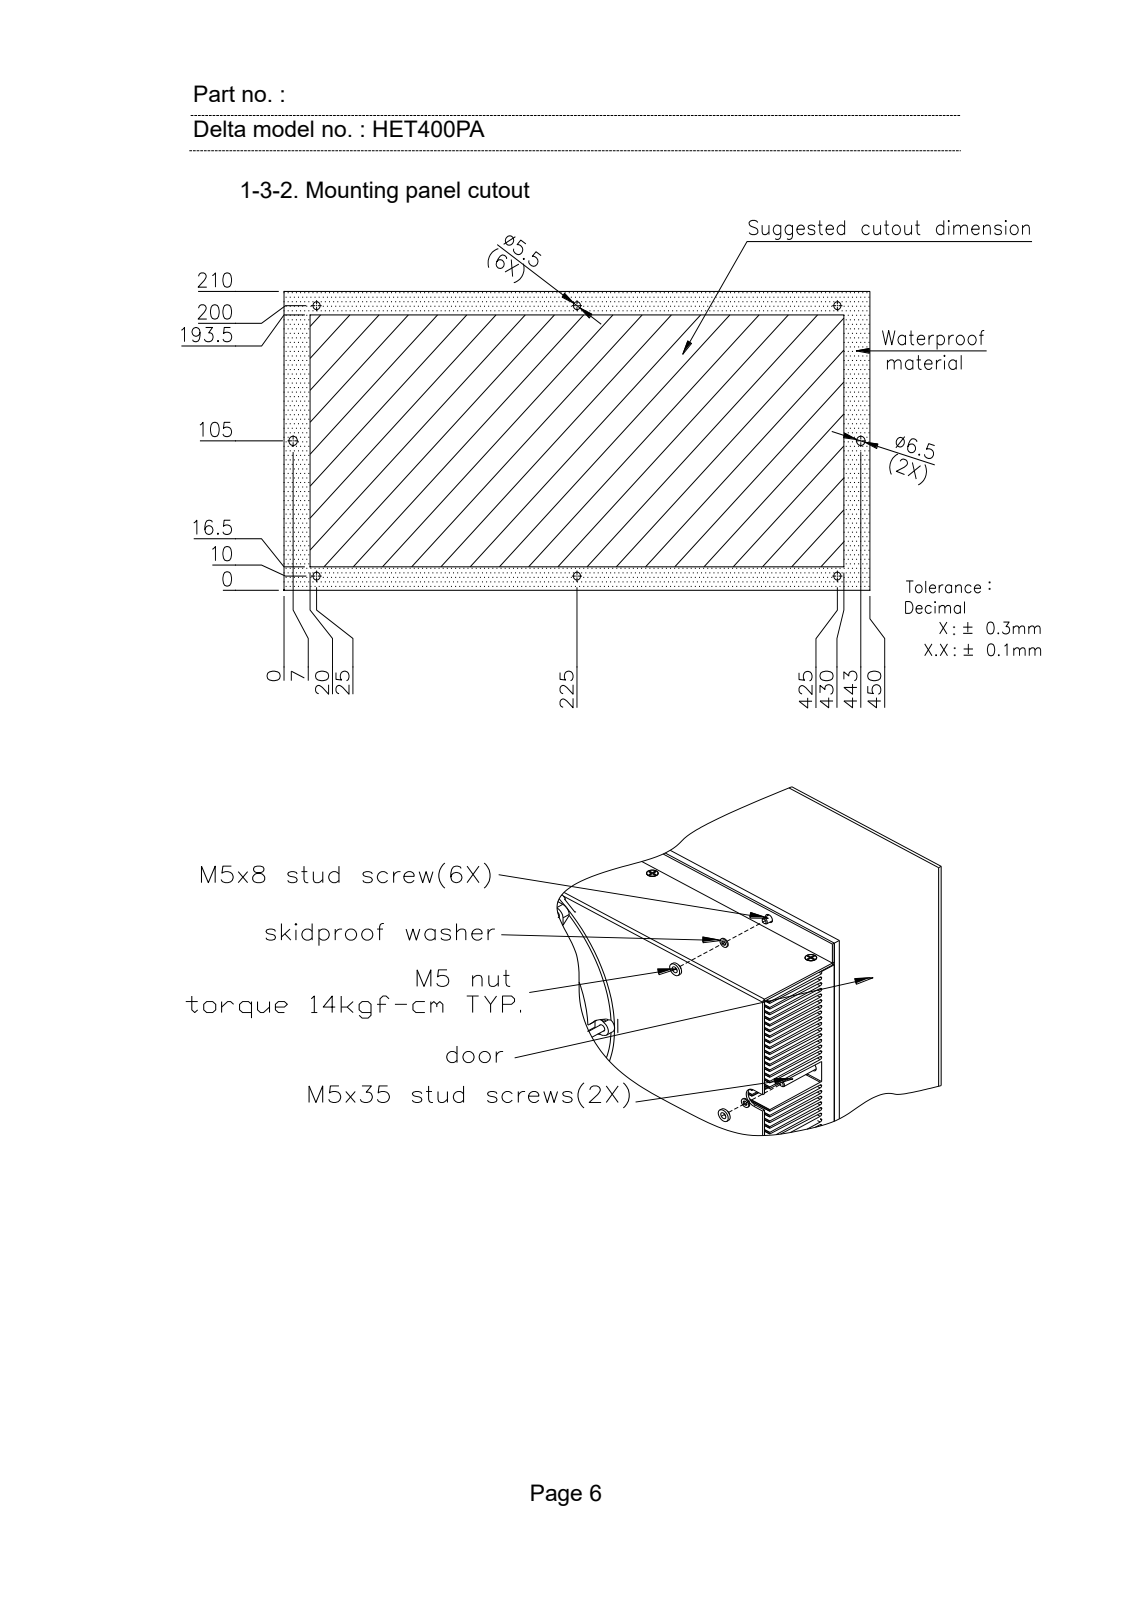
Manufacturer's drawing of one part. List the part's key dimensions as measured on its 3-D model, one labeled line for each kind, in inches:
Part name (STEP PRODUCT): MODULE_ALL_01; HET400PA_3D_OUTLINE_V1_20201019_ASM
STEP written by: CREO PARAMETRIC BY PTC INC, 2015290 (CONFIG_CONTROL_DESIGN)
Units: inches
Bodies: 1 solid, 341 faces (153 planar, 140 cylindrical, 48 other)
Overall size (bounding box): 17.717 × 8.947 × 8.268
Volume: 207.8 in³ · Surface area: 1 194 in²
Round holes (diameter × count): ⌀0.217 ×6, ⌀0.157 ×5, ⌀0.098 ×4, ⌀0.118 ×4, ⌀0.177 ×4, ⌀0.315 ×1, ⌀6.457 ×1
Round bosses / shafts (diameter × count): ⌀6.772 ×1
Partial cylindrical surfaces — rounded edges, fillets, slot ends (radius × count): R0.079 ×20, R0.012 ×6, R0.059 ×6, R0.071 ×6, R0.217 ×4, R0.335 ×4, R0.394 ×4, R0.217 ×2
Main face-to-face distances: 0.059, 4.5, 6.752, 2.177, 0.197, 2.382, 2.579, 2.323, 4.559, 1.98
Hole centre spacings: 3.189, 4.915, 5.995, 7.874, 8.717, 10.861, 11.678, 0.315
